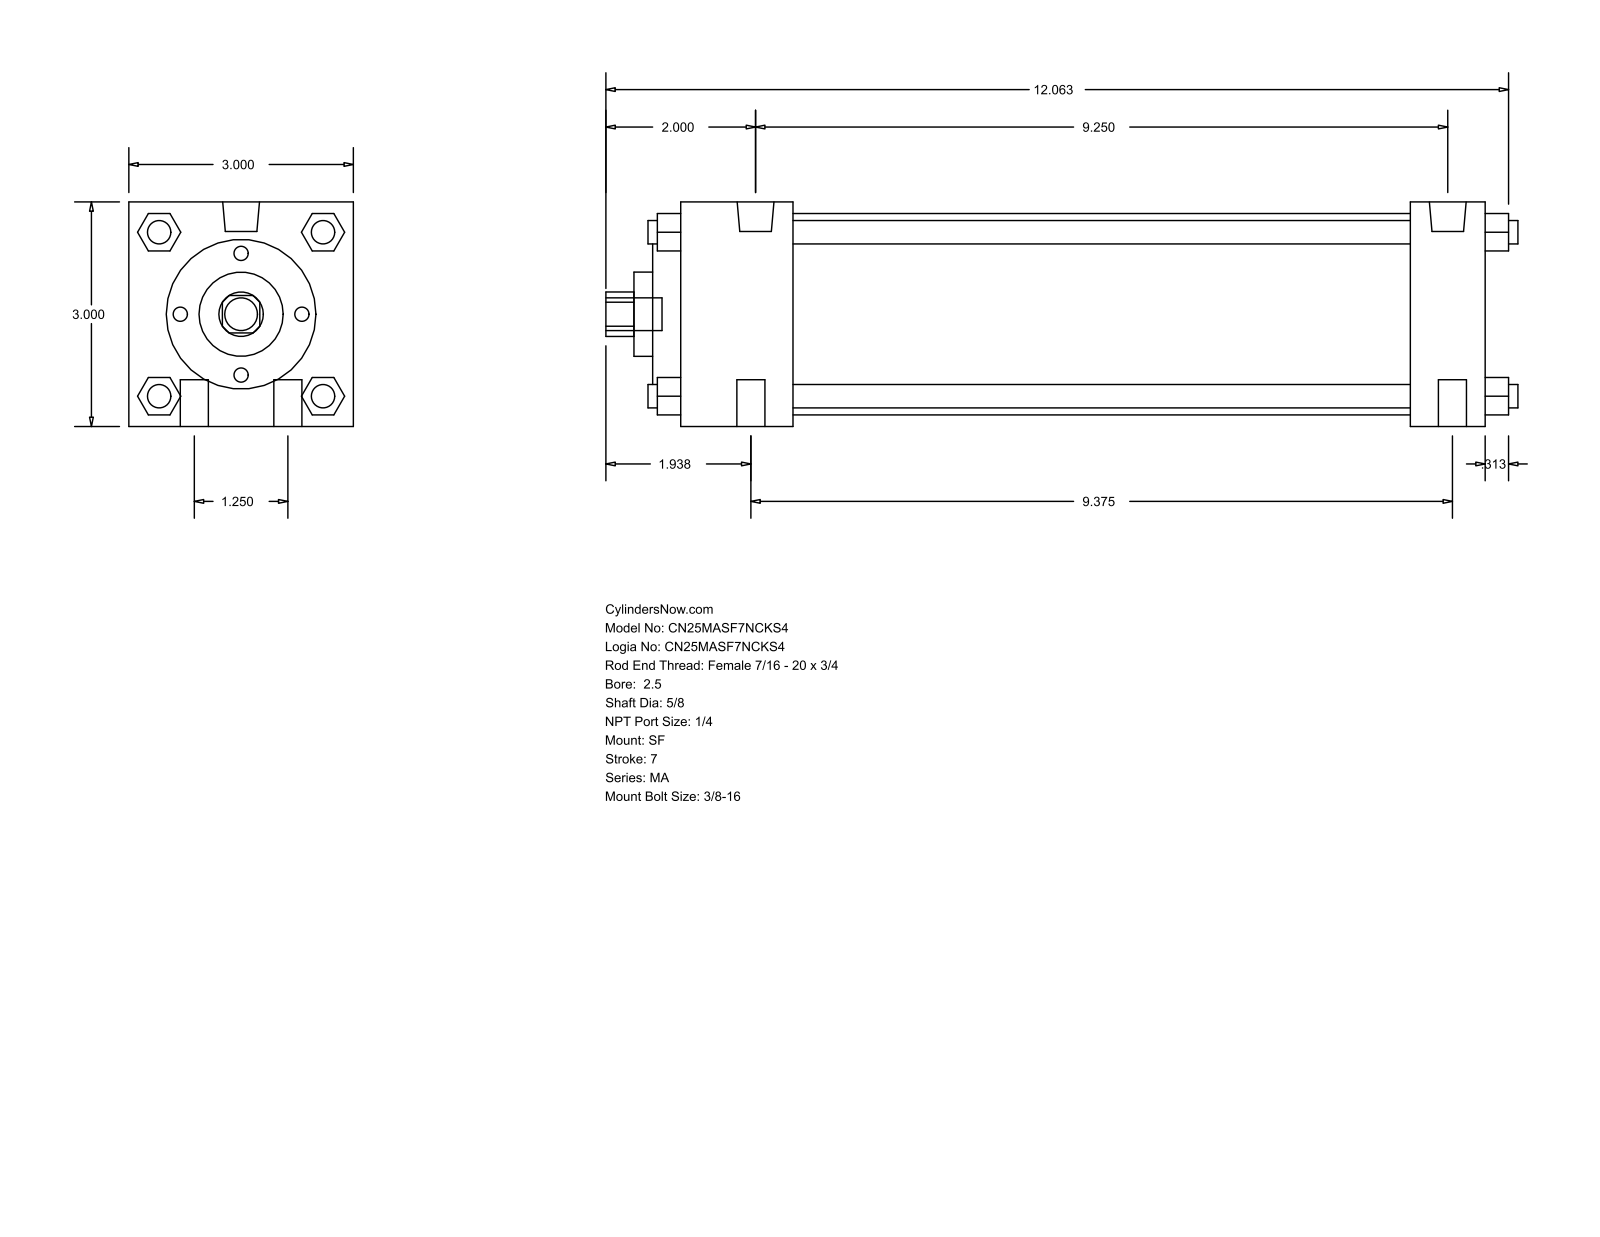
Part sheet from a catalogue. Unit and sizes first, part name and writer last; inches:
Units: inches
Overall size (bounding box): 12.187 × 3 × 3
Round holes (diameter × count): ⌀0.625 ×1, ⌀1.125 ×1, ⌀2 ×1, ⌀2.69 ×1
Round bosses / shafts (diameter × count): ⌀0.313 ×6, ⌀0.375 ×4, ⌀0.492 ×2, ⌀0.437 ×1
Partial cylindrical surfaces — rounded edges, fillets, slot ends (radius × count): R0.297 ×1
Main face-to-face distances: 3, 10.75, 1, 9.75, 1.5, 8.25, 9.25, 0.5, 0.375, 1.875
Bodies: 0 solids, 126 faces (95 planar, 31 cylindrical, 0 other)
Part name (STEP PRODUCT): MA_SF__0250_0.625
STEP written by: GSSL Pune (CONFIG_CONTROL_DESIGN)
